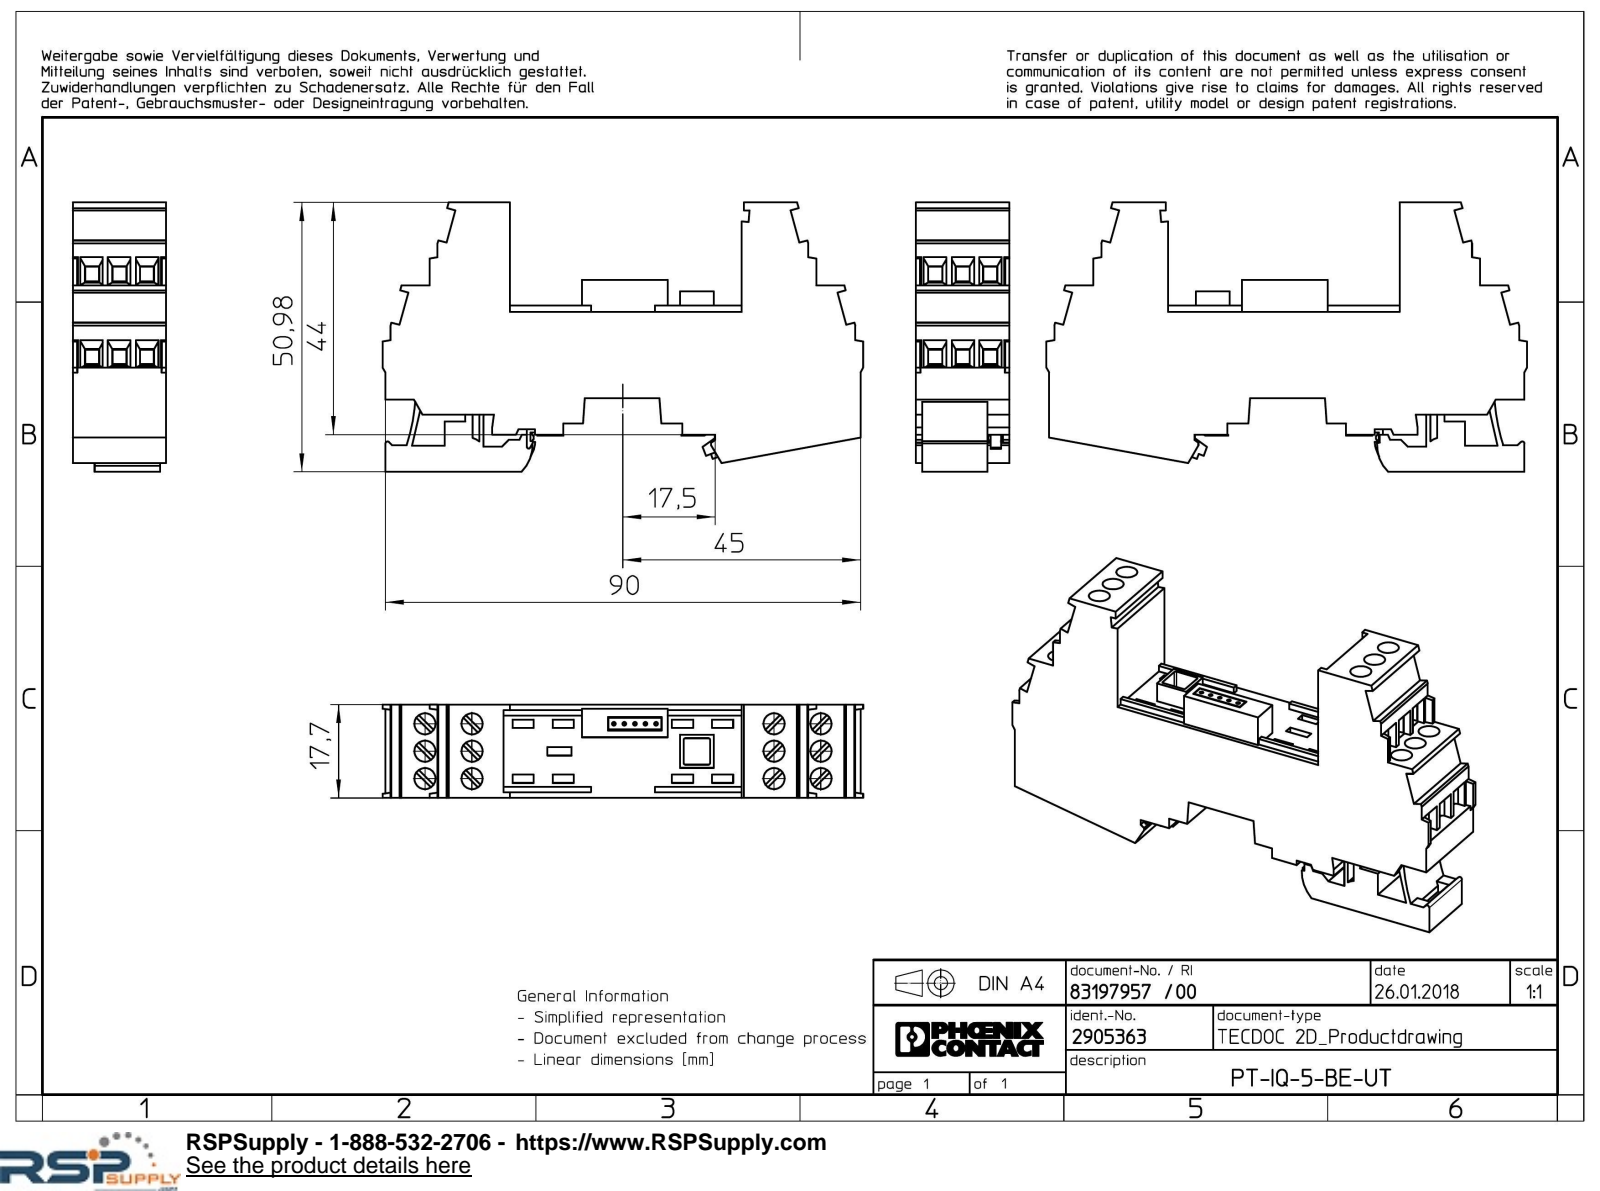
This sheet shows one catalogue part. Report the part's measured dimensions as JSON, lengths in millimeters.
{"part_name": "PT_IQ_5_BE_UT-select", "step_written_by": "Creo Elements/Direct Modeling 18.1I 14-Aug-2016 (C) Parametric Technology GmbH (AUTOMOTIVE_DESIGN)", "units": "millimeters", "bodies": {"solids": 1, "faces": 651, "planar": 605, "cylindrical": 45, "other": 1}, "overall_size": [91.05, 50.98, 17.7], "volume_mm3": 44652, "surface_area_mm2": 15924, "round_holes": [[4, 12], [0.7, 5]], "partial_cylinders_radius": [[0.3, 5], [0.4, 1], [4, 1], [9.5, 1], [36.42, 1]], "face_to_face_distances": [17.7, 2.1, 15.7, 3.1, 3.8, 30.28, 16.33, 2.6, 45.1, 50.98], "hole_center_spacings": [5.2, 10.31, 66.3, 8.9, 66.1, 2, 10.4, 13.69]}
